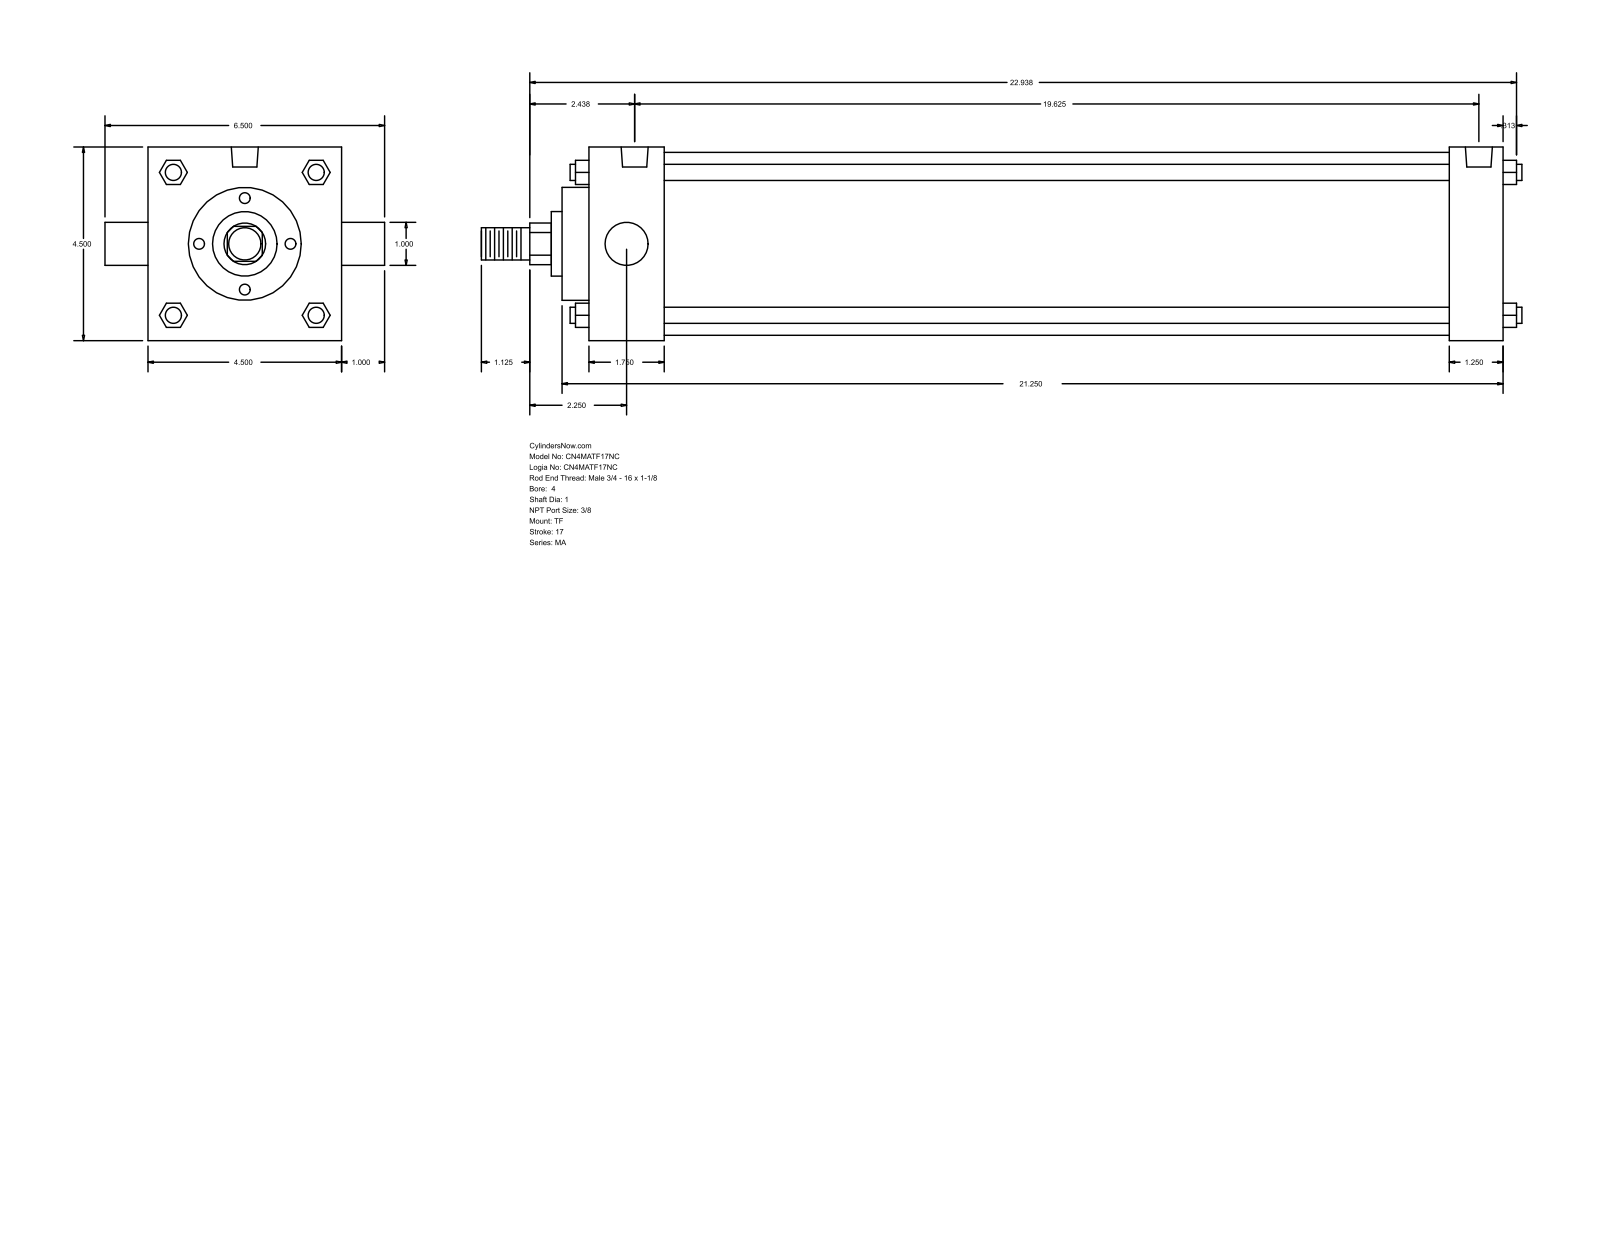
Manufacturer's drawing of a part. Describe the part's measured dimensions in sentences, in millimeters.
The part is named "MA_TF__0400_1". Its 3-D file was written by "GSSL Pune (CONFIG_CONTROL_DESIGN)". It is 0 solids with 122 faces: 93 planar, 29 cylindrical and 0 other. Overall it measures 614.36 by 165.1 by 114.3 millimeters. Round holes: 3 of diameter 11.11, 2 of diameter 15.93. Round bosses or shafts: 4 of diameter 9.53, 2 of diameter 25.4, 1 of diameter 107.95, 1 of diameter 66.67, 1 of diameter 38.1, 1 of diameter 19.05. Partial cylindrical surfaces (rounded edges, fillets, slot ends): 1 of radius 12.29. The main face-to-face distances are 114.3, 539.75, 508, 31.75, 44.46, 463.54, 495.29, 555.62, 15.87, 60.33. The hole center spacings are 4.76, 4.77, 488.95, 493.71, 493.72, 498.48.
